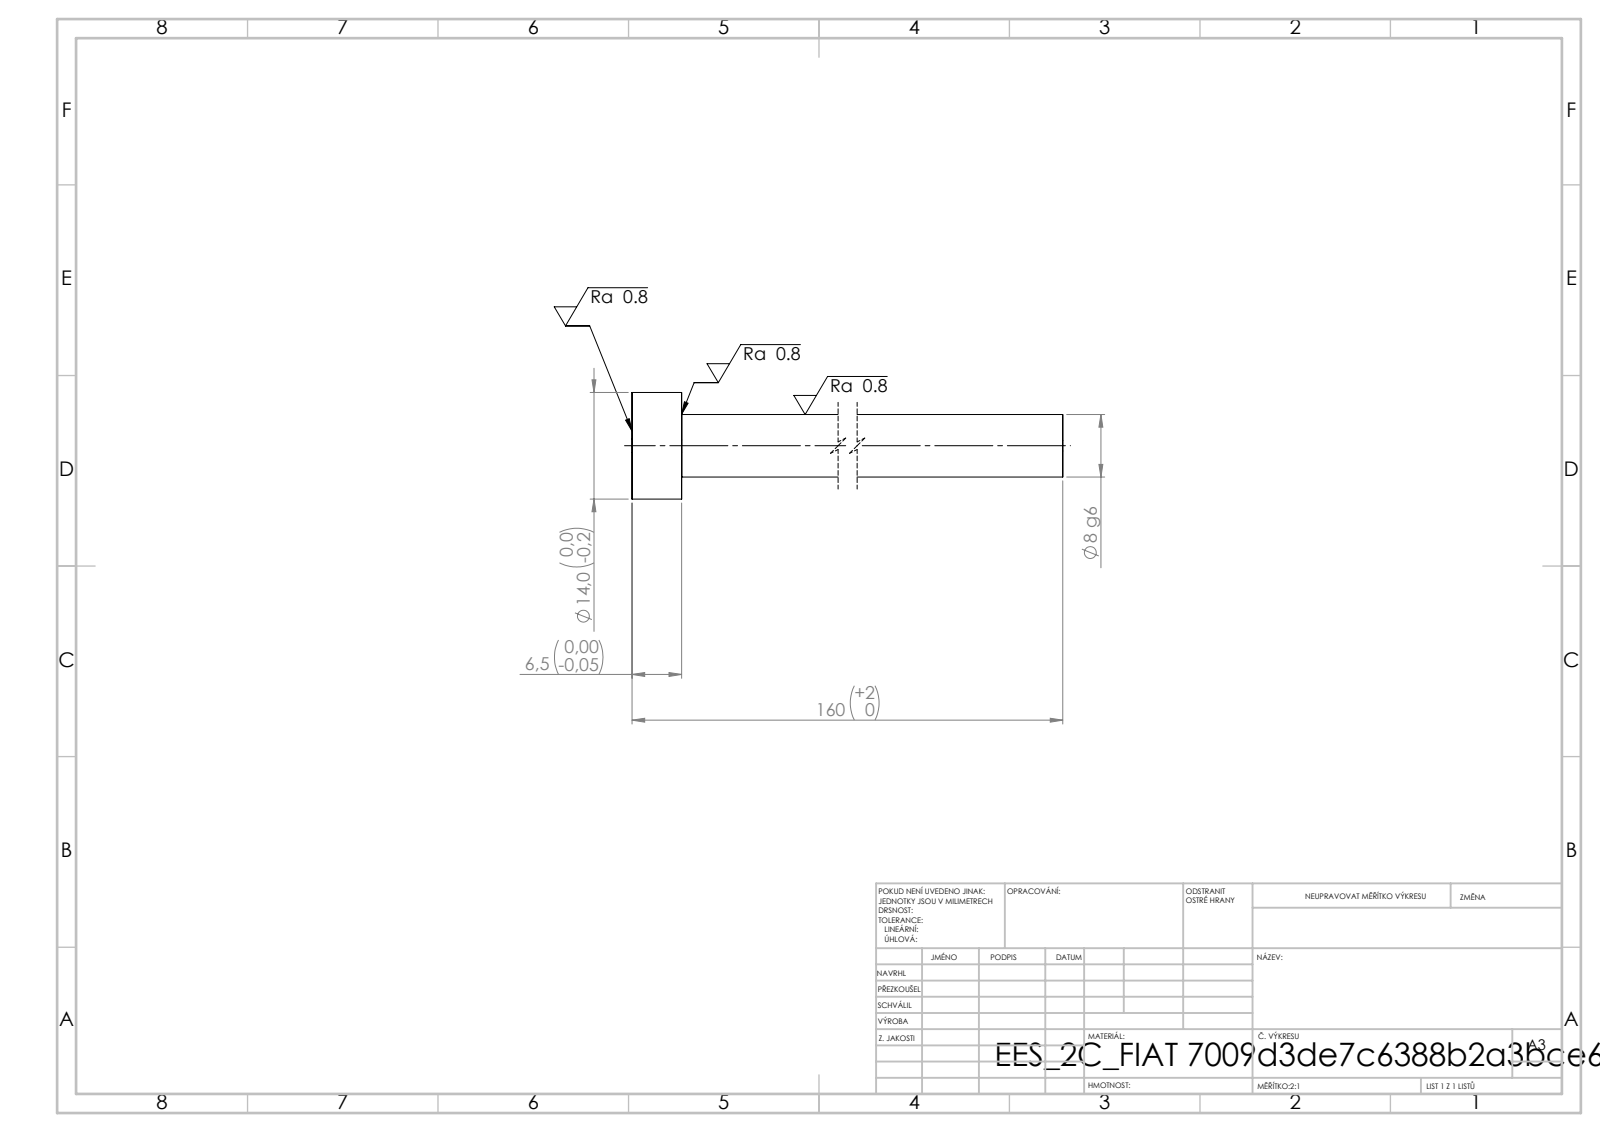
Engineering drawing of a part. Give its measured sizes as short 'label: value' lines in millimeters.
written by: SolidWorks 2019 (CONFIG_CONTROL_DESIGN)
unit: mm
bodies: 1 solid, 7 faces (3 planar, 4 cylindrical, 0 other)
size: 160 × 14 × 14
volume: 9 107 mm³; area: 4 548 mm²
bosses: 1× ⌀14, 1× ⌀8.2
face distances: 6.5, 160, 153.5
